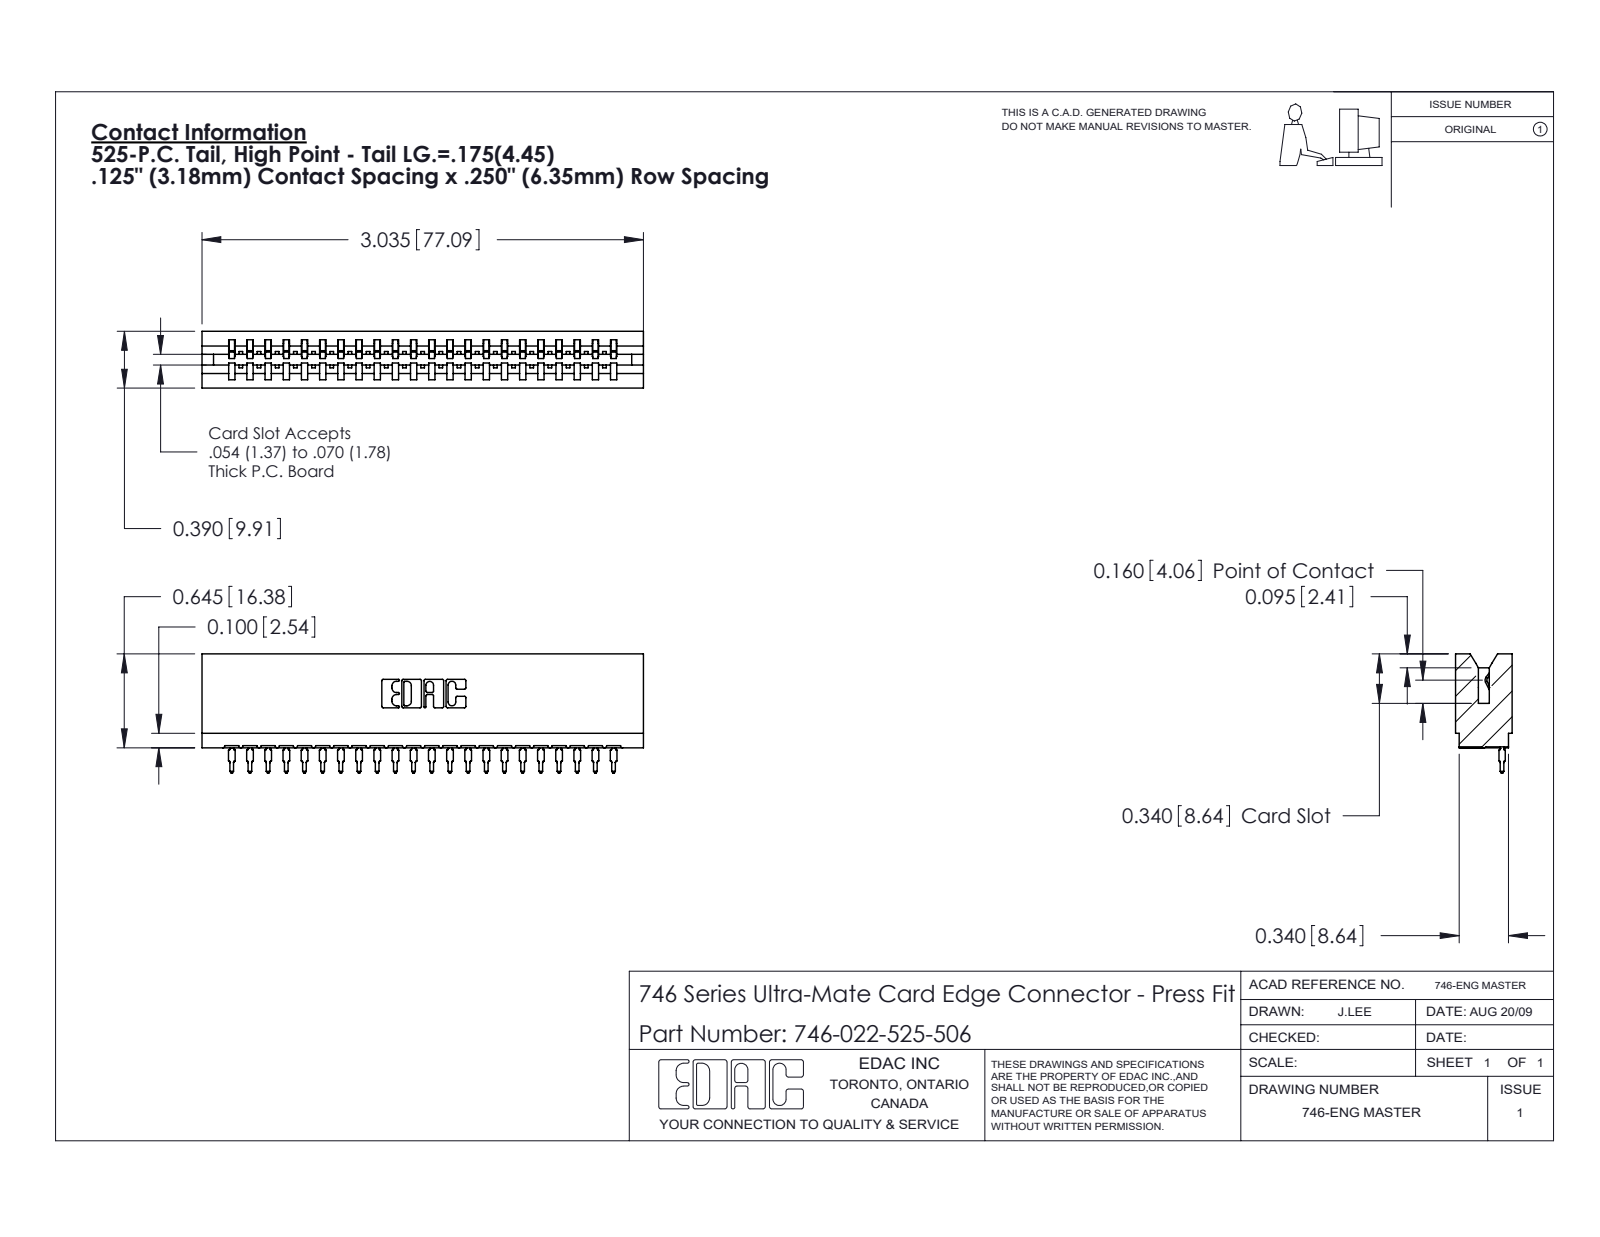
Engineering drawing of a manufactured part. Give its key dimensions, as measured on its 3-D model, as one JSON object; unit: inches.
{"part_name": "746-022-525-506; 746 Part_.340 Slot Depth - 06; 746-292-001_525", "step_written_by": "SolidWorks 2020 (CONFIG_CONTROL_DESIGN)", "units": "inches", "bodies": {"solids": 23, "faces": 2474, "planar": 1442, "cylindrical": 460, "other": 572}, "overall_size": [3.035, 0.819, 0.39], "volume_in3": 0.533, "surface_area_in2": 17.61, "partial_cylinders_radius": [[0.021, 44], [0.015, 23], [0.01, 22], [0.007, 6], [0.031, 6], [0.005, 4], [0.011, 4], [0.026, 3]], "face_to_face_distances": [0.25, 0.057, 0.333, 0.39, 0.5, 0.042, 0.125, 0.025, 0.307, 0.292]}
